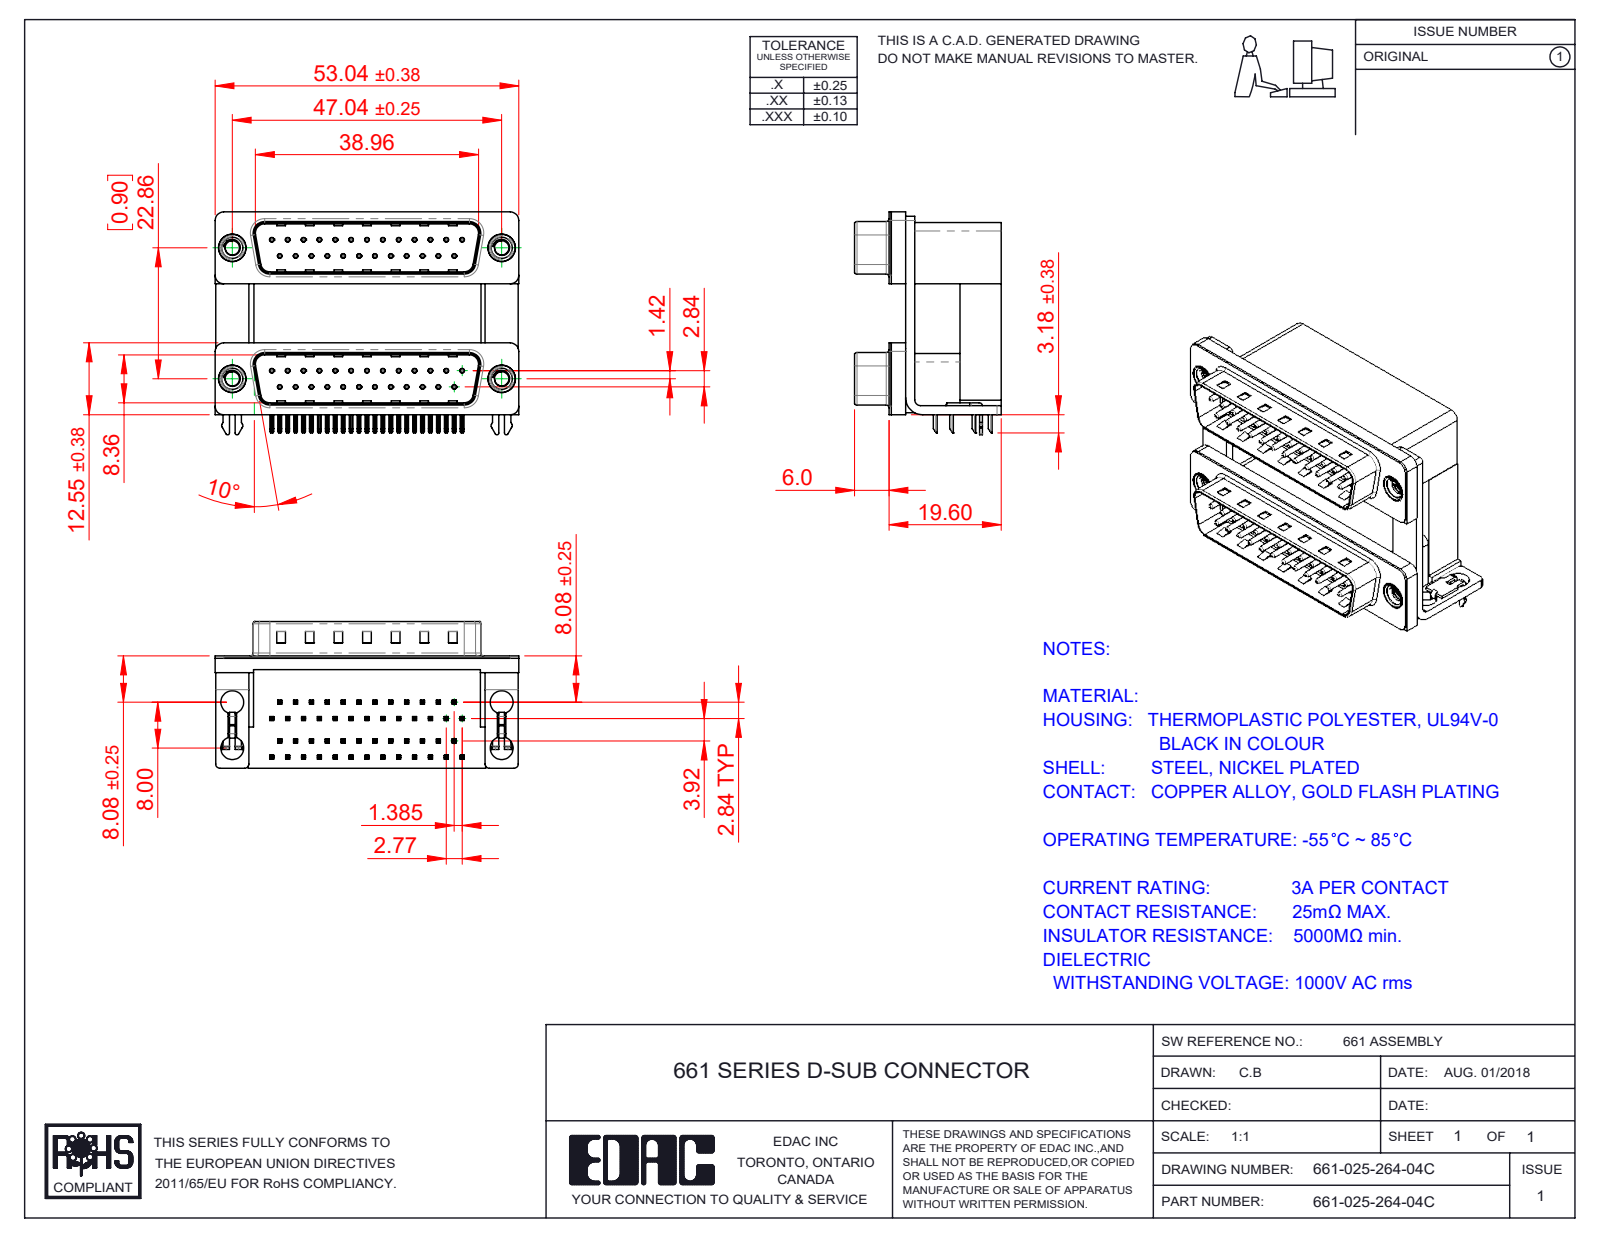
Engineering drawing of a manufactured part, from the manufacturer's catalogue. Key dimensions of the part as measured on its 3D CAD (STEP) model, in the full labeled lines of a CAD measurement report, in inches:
Part name (STEP PRODUCT): 661 Threaded Rivet_M3; 661 Contact Top Lower; 661 Contact Bottom Lower; 661 Contact Top Upper_H (+8 more)
STEP written by: SolidWorks 2020 (CONFIG_CONTROL_DESIGN)
Units: inches
Bodies: 63 solids, 4726 faces (3016 planar, 1320 cylindrical, 390 other)
Overall size (bounding box): 2.088 × 1.532 × 1.008
Volume: 1.363 in³ · Surface area: 36.13 in²
Round holes (diameter × count): ⌀0.014 ×50, ⌀0.031 ×50, ⌀0.157 ×8, ⌀0.098 ×4, ⌀0.138 ×4, ⌀0.189 ×4, ⌀0.197 ×4
Round bosses / shafts (diameter × count): ⌀0.03 ×50, ⌀0.193 ×4, ⌀0.187 ×4, ⌀0.154 ×4
Partial cylindrical surfaces — rounded edges, fillets, slot ends (radius × count): R0.01 ×206, R0.005 ×100, R0.02 ×20, R0.059 ×14, R0.03 ×10, R0.035 ×8, R0.063 ×8, R0.079 ×8
Main face-to-face distances: 0.472, 0.9, 0.756, 0.016, 0.283, 0.421, 0.488, 0.657, 0.374, 0.098
Hole centre spacings: 0.124, 0.109, 0.218, 0.327, 0.436, 0.545, 0.654, 0.198
